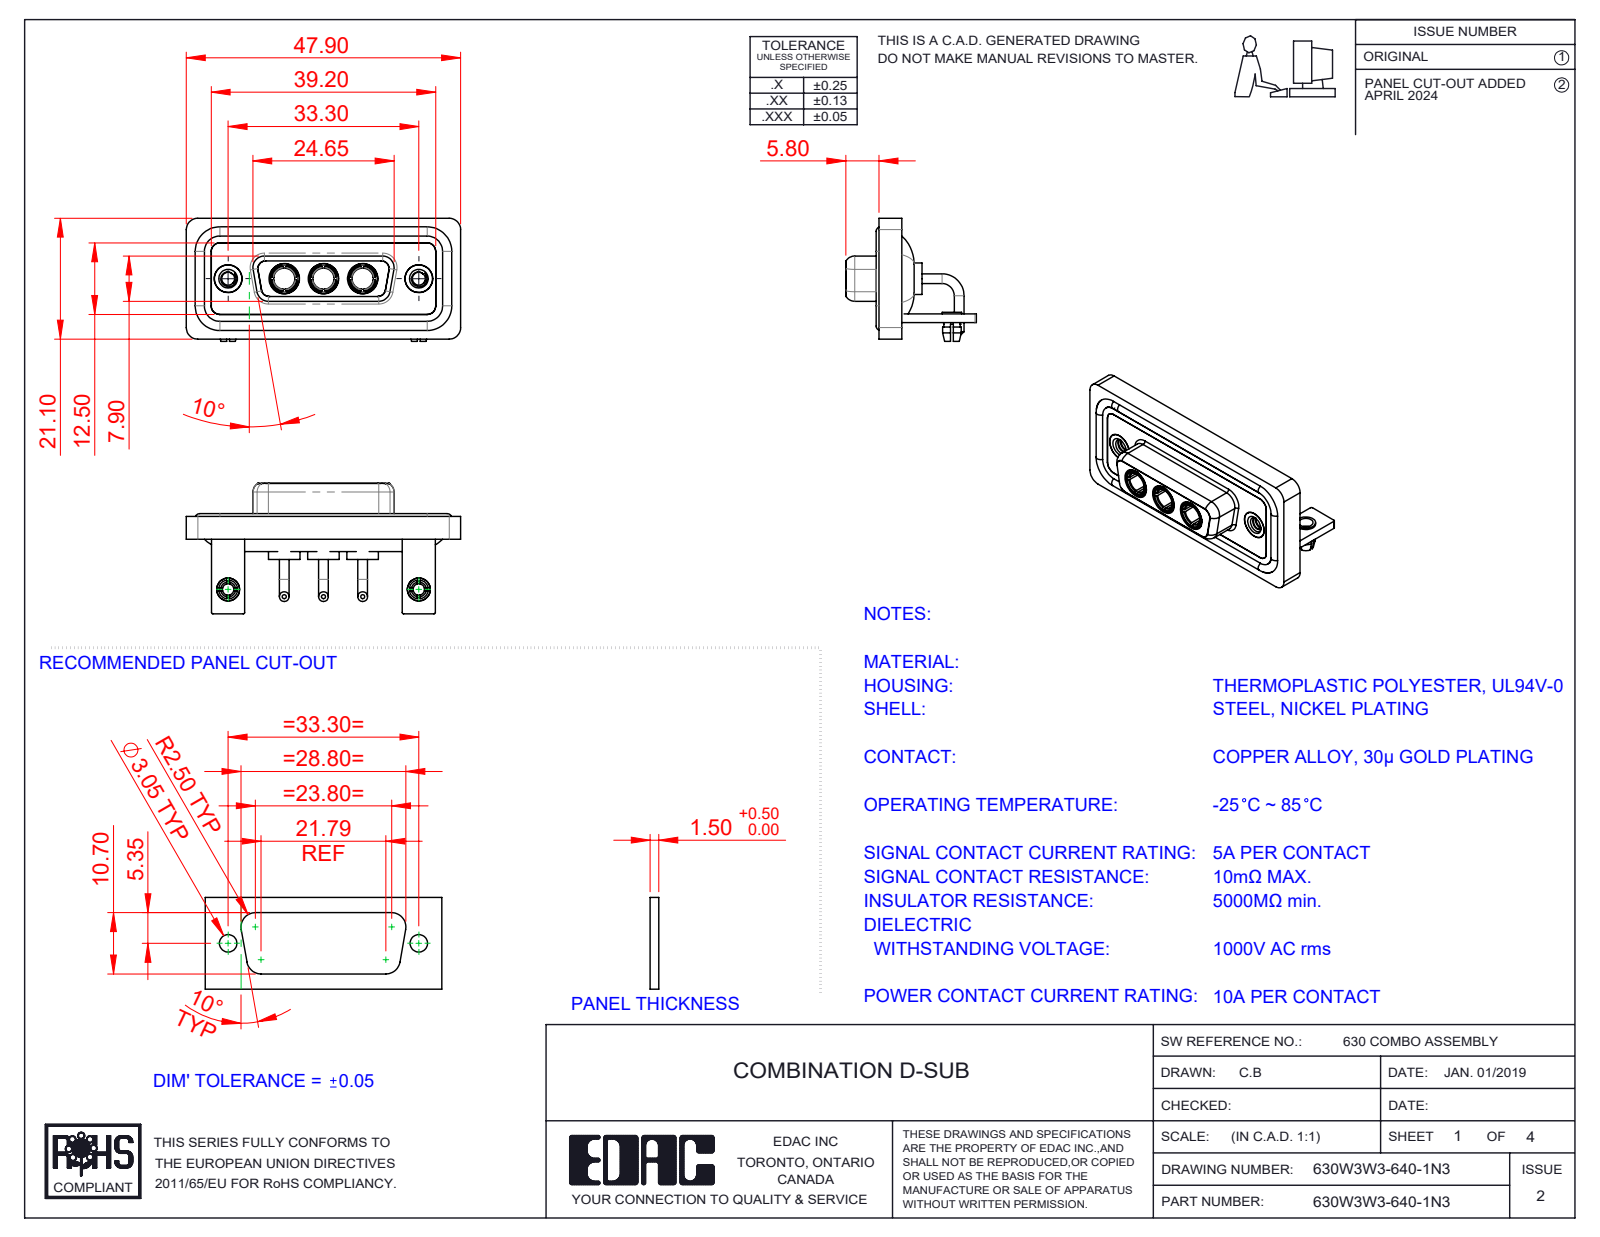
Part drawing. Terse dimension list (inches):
name: 630W3W3-640-1N3; 630Combo Housing_3W3; Power Socket_10A RA; 630Combo Shell Rear_15 Contacts (+5 more)
written by: SolidWorks 2023 (CONFIG_CONTROL_DESIGN)
unit: in
bodies: 17 solids, 760 faces (260 planar, 319 cylindrical, 181 other)
size: 1.886 × 0.898 × 0.846
volume: 0.391 in³; area: 16.69 in²
holes: 5× ⌀0.191, 3× ⌀0.146, 3× ⌀0.209, 2× ⌀0.079, 2× ⌀0.089, 2× ⌀0.098, 2× ⌀0.126, 2× ⌀0.157, 2× ⌀0.159, 2× ⌀0.197
bosses: 6× ⌀0.067, 4× ⌀0.063, 3× ⌀0.217, 3× ⌀0.205, 3× ⌀0.195, 3× ⌀0.187, 3× ⌀0.148, 2× ⌀0.195
rounds: 21× R0.079, 18× R0.059, 16× R0.01, 12× R0.053, 8× R0.063, 5× R0.02, 4× R0.024, 4× R0.026
face distances: 0.016, 0.114, 0.059, 0.071, 0.146, 0.043, 0.161, 0.063, 0.098, 0.055
hole spacings: 0.27, 0.386, 0.656, 0.925, 1.311, 0.539
